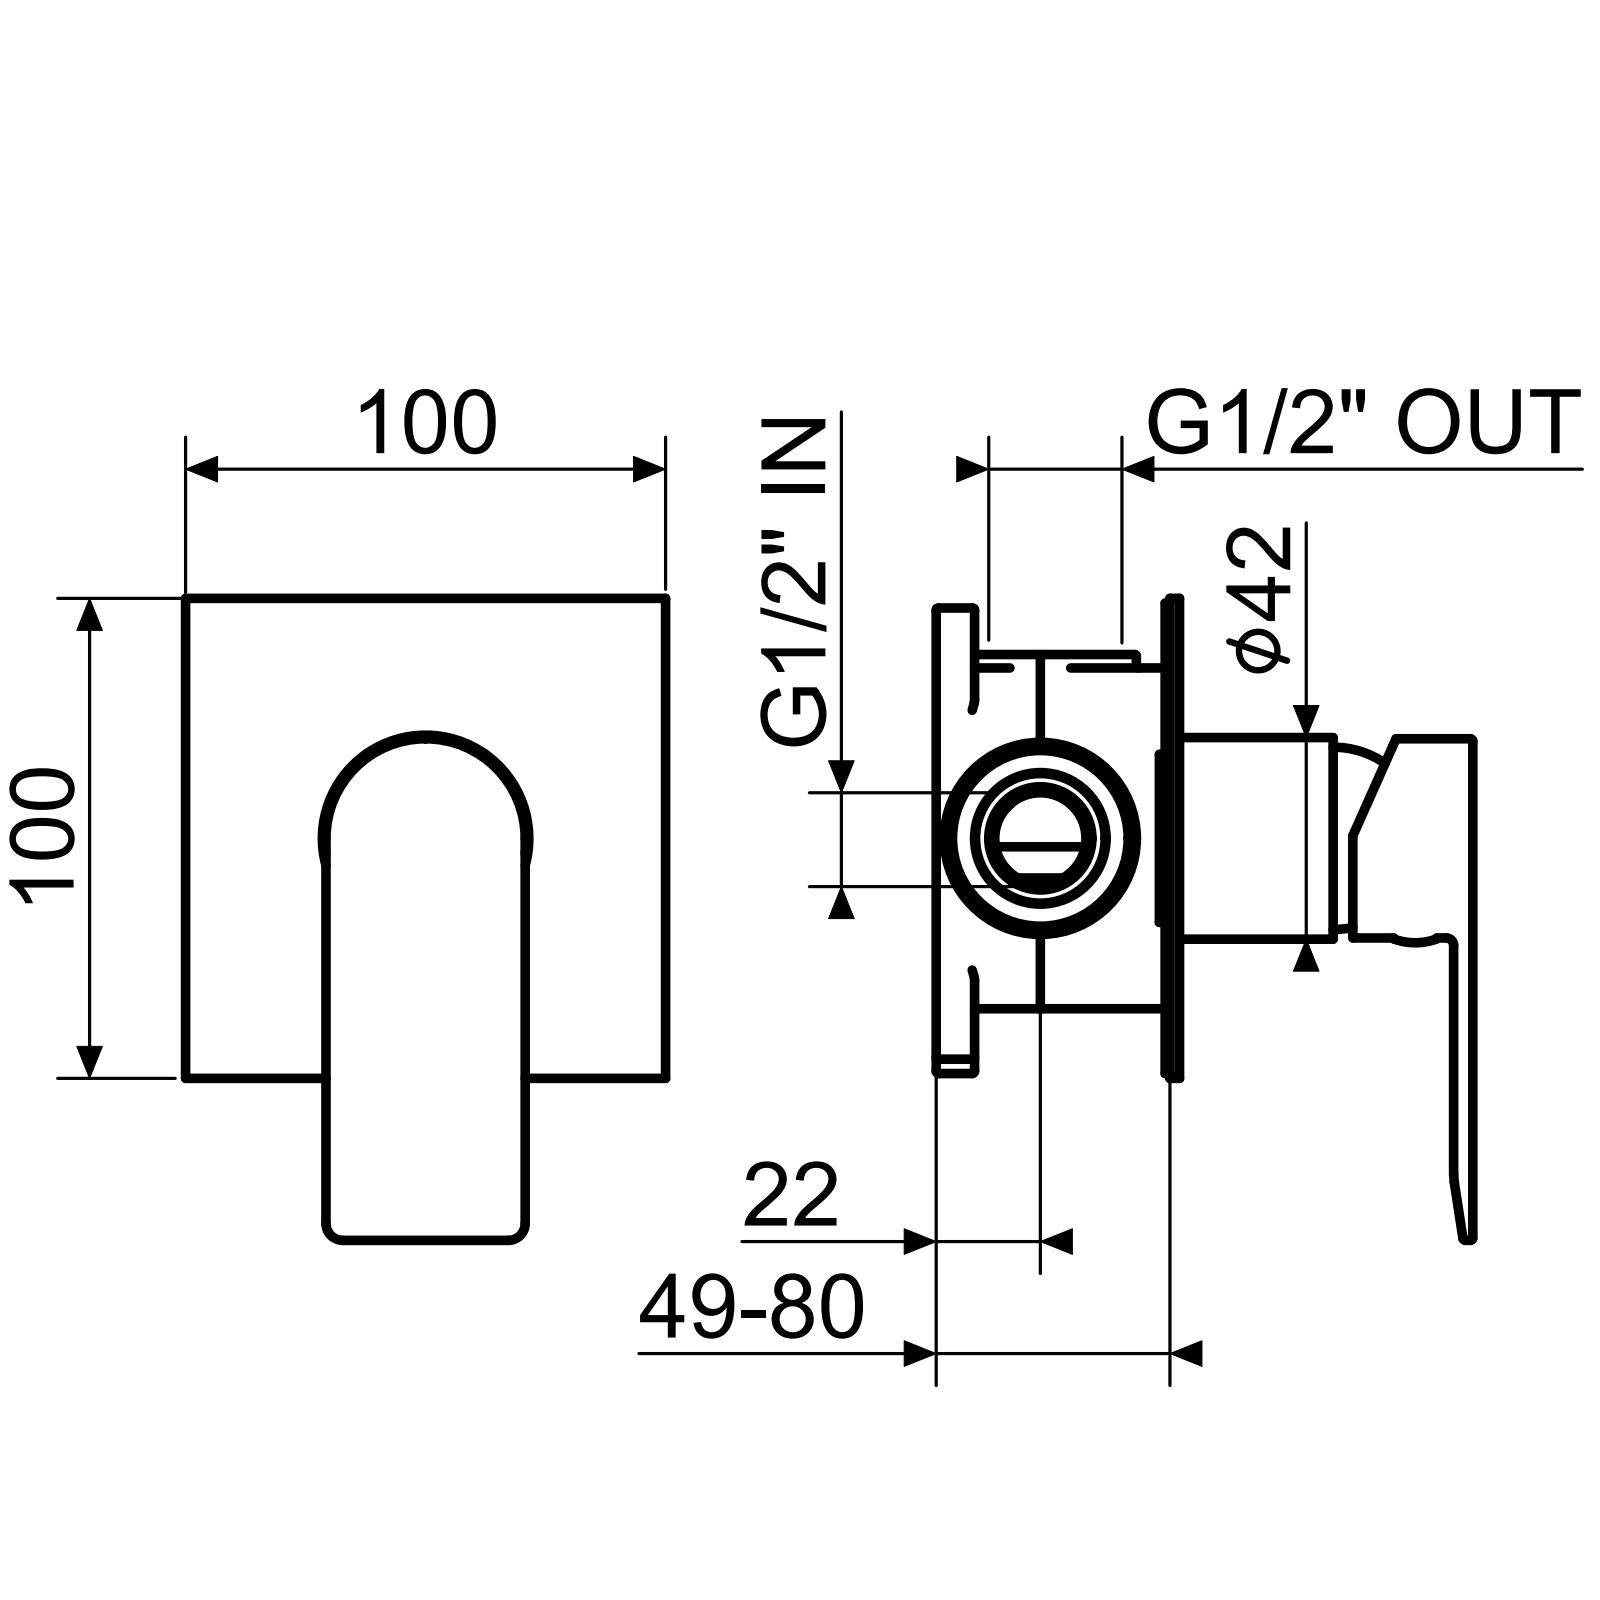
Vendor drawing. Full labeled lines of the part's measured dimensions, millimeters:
Part name (STEP PRODUCT): SINMAC0008; SCCMAC0005; AAYA005C001; SPLMAC0001 (+4 more)
STEP written by: CREO PARAMETRIC BY PTC INC, 2020281 (CONFIG_CONTROL_DESIGN)
Units: millimetres
Bodies: 6 solids, 218 faces (68 planar, 55 cylindrical, 95 other)
Overall size (bounding box): 133.75 × 100 × 67.1
Volume: 42 989 mm³ · Surface area: 49 158 mm²
Round holes (diameter × count): ⌀4.2 ×1, ⌀6.5 ×1, ⌀8 ×1, ⌀29 ×1, ⌀32.75 ×1, ⌀34.5 ×1, ⌀40 ×1, ⌀43 ×1, ⌀43.5 ×1, ⌀46.5 ×1
Round bosses / shafts (diameter × count): ⌀49 ×1, ⌀42 ×1, ⌀41.5 ×1, ⌀34 ×1, ⌀5 ×1
Partial cylindrical surfaces — rounded edges, fillets, slot ends (radius × count): R0.5 ×6, R1 ×4, R10 ×3, R0.3 ×2, R1.5 ×2, R3.5 ×2
Main face-to-face distances: 2, 63.1, 61.1, 4, 60.7, 58.7, 2.4, 6, 64.7, 67.1
